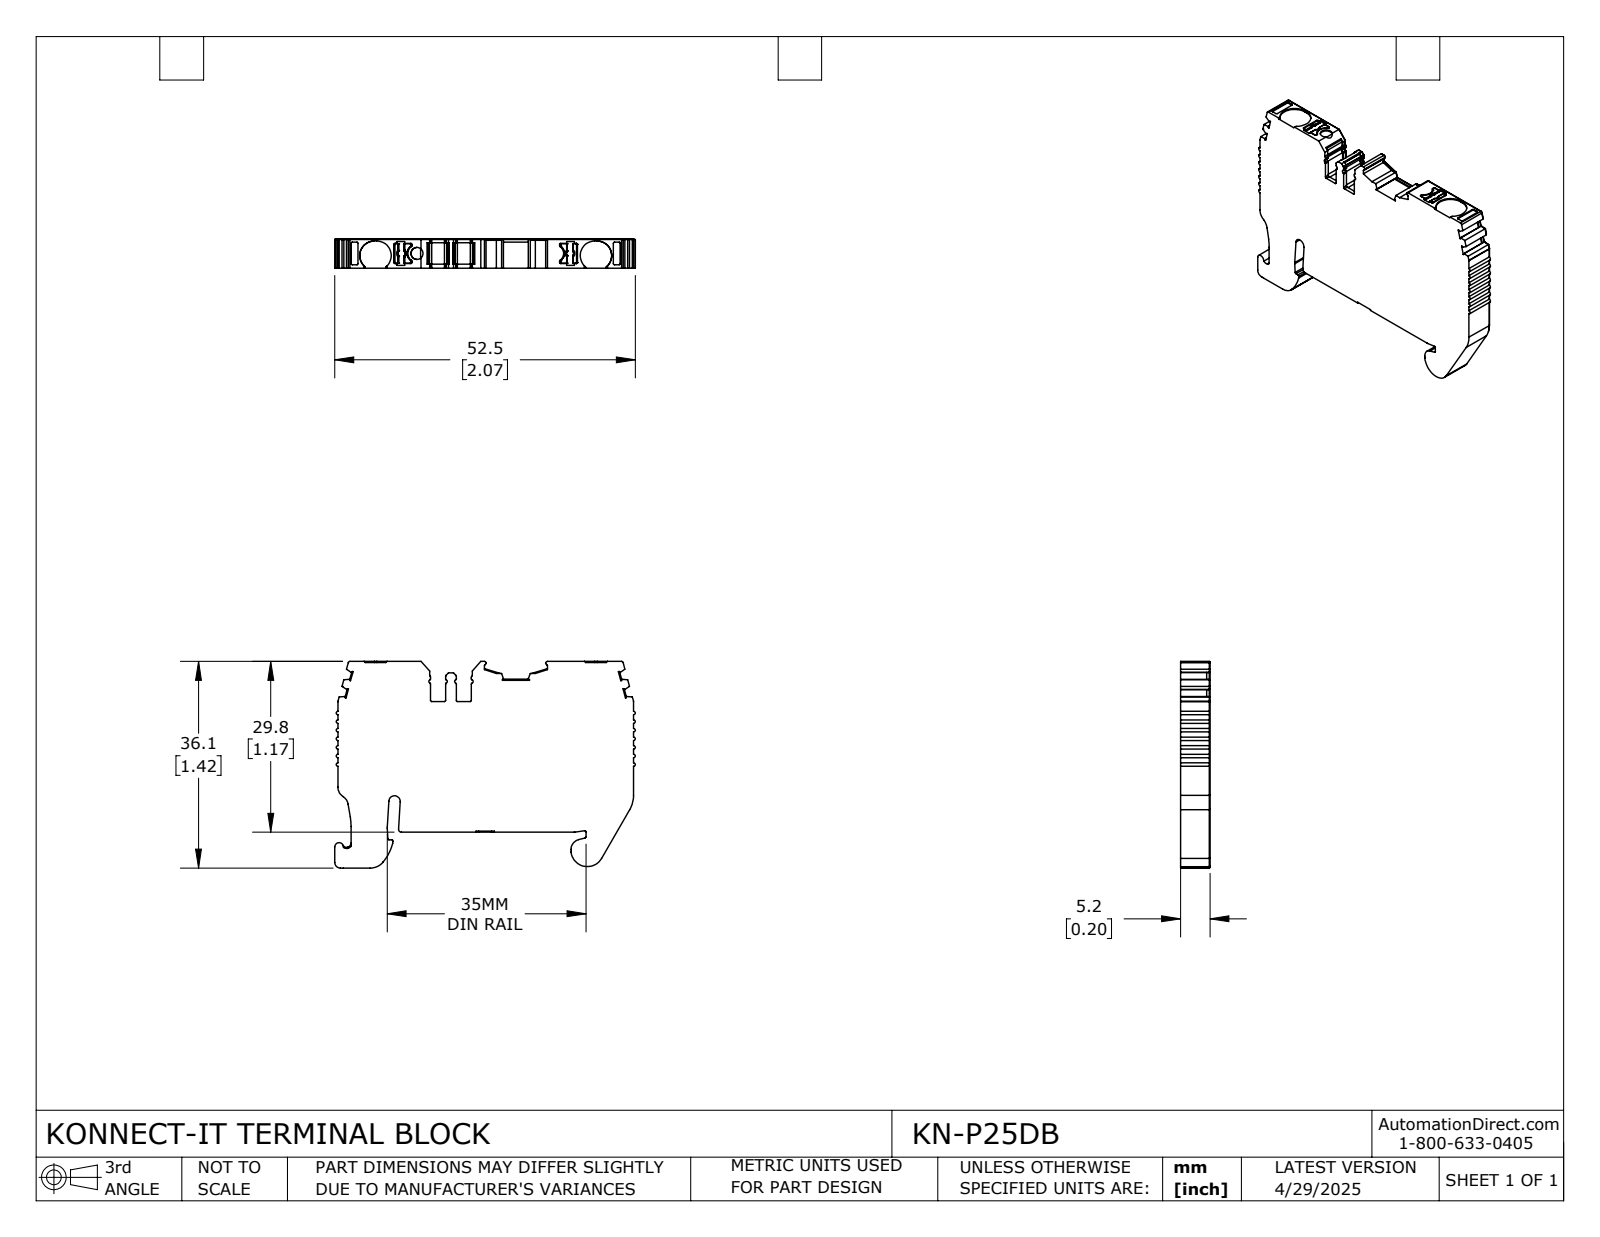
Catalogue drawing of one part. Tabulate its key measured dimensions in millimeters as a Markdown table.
| quantity | value |
| --- | --- |
| part name | KN-P25DB |
| STEP written by | SolidWorks 2024 (CONFIG_CONTROL_DESIGN) |
| units | millimeters |
| bodies | 1 solid, 582 faces (308 planar, 239 cylindrical, 35 other) |
| overall size | 52.48 × 36.07 × 5.15 |
| volume | 7 676 mm³ |
| surface area | 4 278 mm² |
| round holes (diameter × count) | 2.1 × 1 |
| partial cylindrical surfaces (radius × count) | 0.2 × 54, 0.3 × 39, 0.5 × 18, 0.1 × 17, 0.4 × 9, 0.15 × 8, 2.55 × 4, 1 × 3 |
| main face-to-face distances | 5.15, 29.61, 29.81, 51.63, 4.5, 5, 6.26, 35.87, 2, 36.07 |
